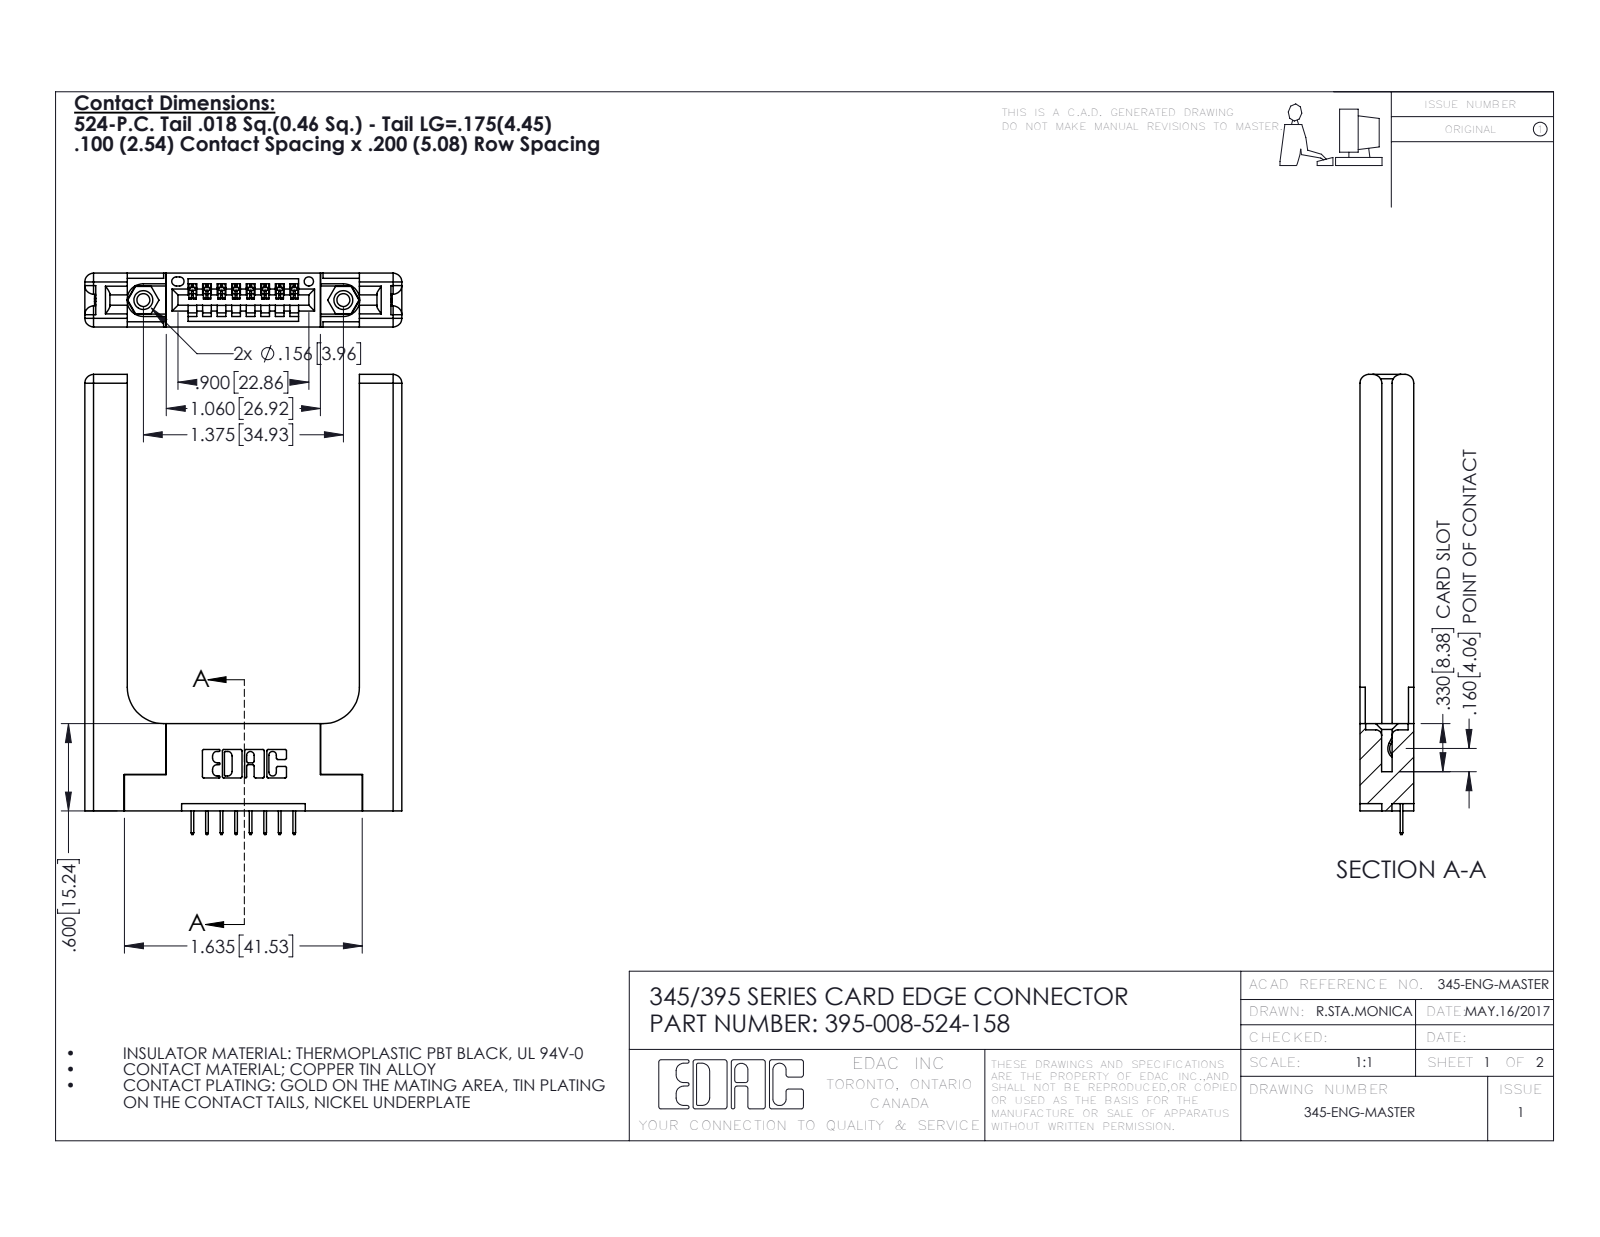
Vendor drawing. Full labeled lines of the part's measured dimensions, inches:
Part name (STEP PRODUCT): 345-292-001_345-293-124; 345-220-058_345-220-058; 345-250-001_345-250-001-102; 345 Part_Flush Mounting Lugs - 0.156 Dia-TH (+1 more)
STEP written by: SolidWorks 2016 (CONFIG_CONTROL_DESIGN)
Units: inches
Bodies: 13 solids, 878 faces (596 planar, 222 cylindrical, 60 other)
Overall size (bounding box): 3.162 × 2.179 × 0.37
Volume: 0.821 in³ · Surface area: 17.54 in²
Round holes (diameter × count): ⌀0.089 ×2, ⌀0.125 ×2, ⌀0.156 ×2, ⌀0.064 ×1
Round bosses / shafts (diameter × count): ⌀0.155 ×2
Partial cylindrical surfaces — rounded edges, fillets, slot ends (radius × count): R0.01 ×22, R0.006 ×16, R0.06 ×16, R0.007 ×6, R0.031 ×6, R0.026 ×3, R0.03 ×2, R0.031 ×2
Main face-to-face distances: 0.37, 0.15, 0.22, 0.072, 0.077, 0.148, 0.298, 1.596, 0.071, 0.2
Hole centre spacings: 0.27, 1.144, 1.375
